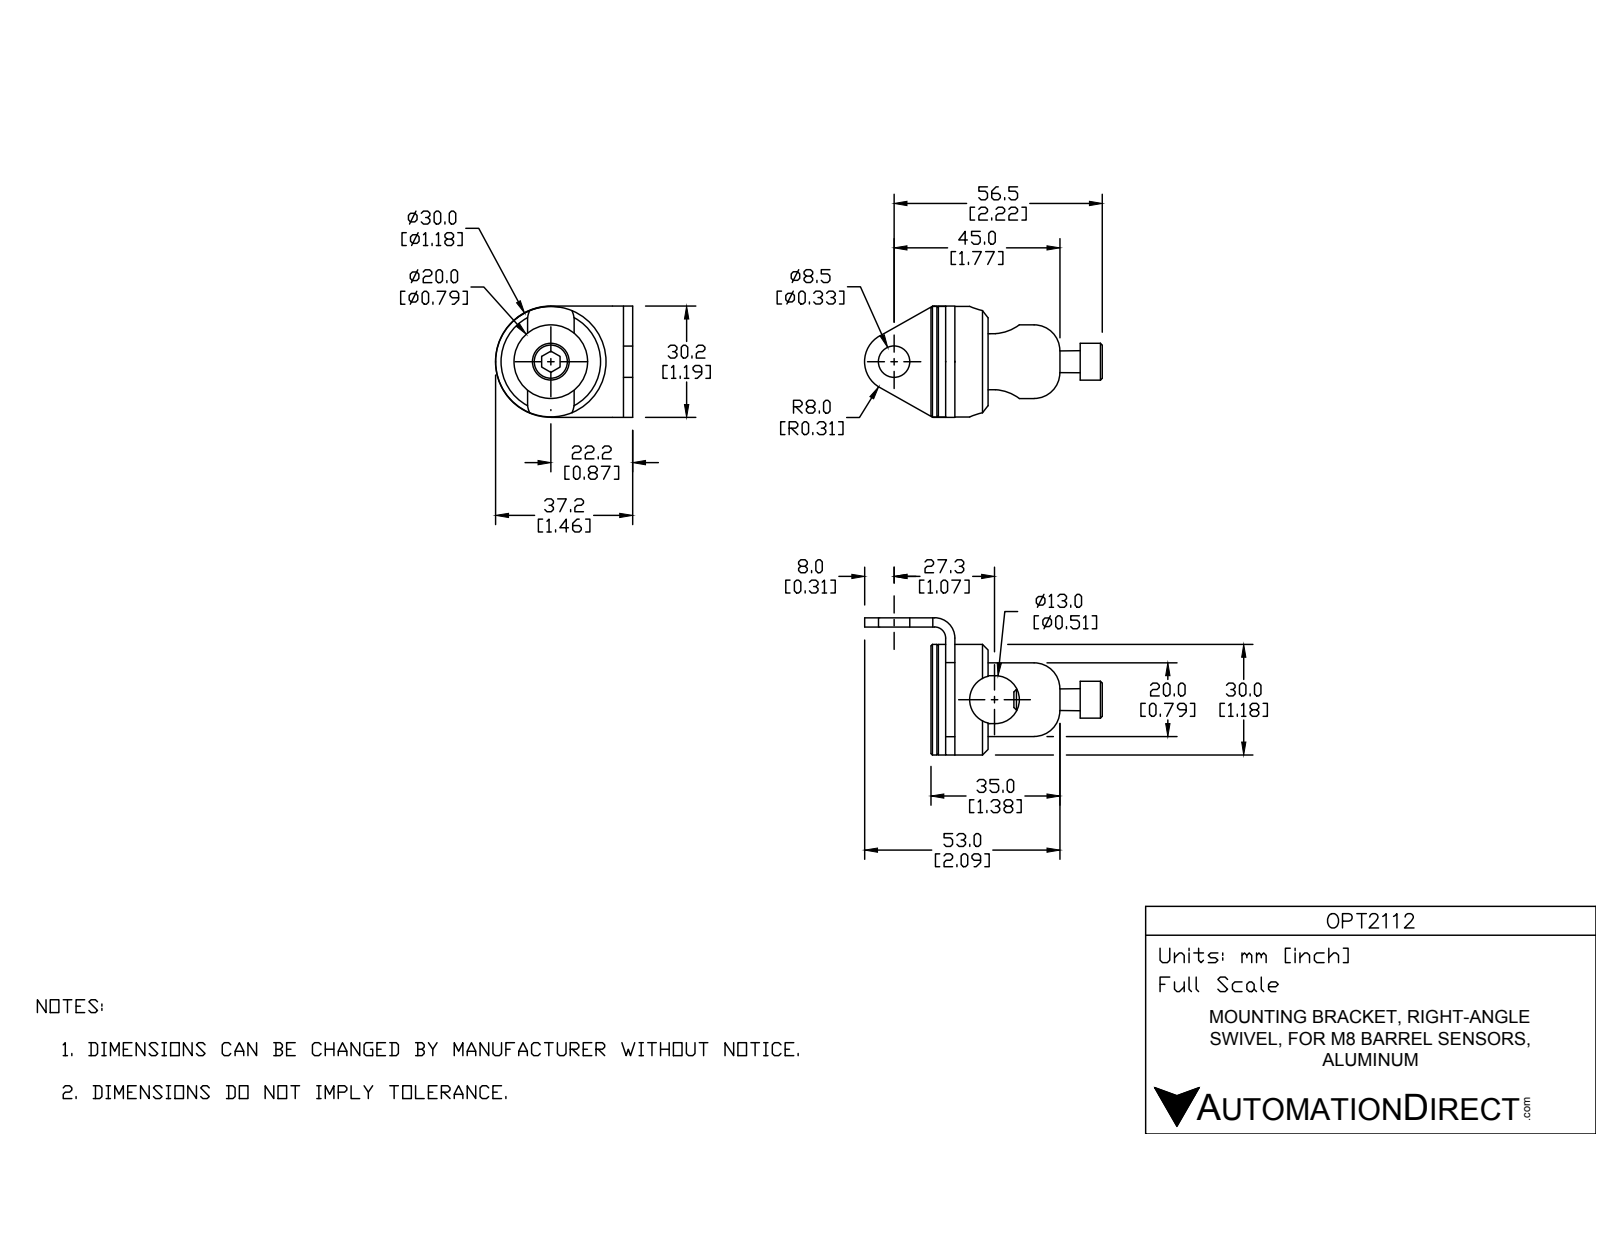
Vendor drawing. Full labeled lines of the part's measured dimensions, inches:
STEP written by: Unknown (CONFIG_CONTROL_DESIGN)
Units: inches
Bodies: 4 solids, 116 faces (58 planar, 40 cylindrical, 18 other)
Overall size (bounding box): 2.539 × 2.059 × 1.78
Volume: 1.864 in³ · Surface area: 26.46 in²
Round holes (diameter × count): ⌀0.335 ×2, ⌀0.791 ×2, ⌀0.787 ×1, ⌀0.827 ×1
Round bosses / shafts (diameter × count): ⌀1.181 ×1, ⌀0.394 ×1
Partial cylindrical surfaces — rounded edges, fillets, slot ends (radius × count): R0.591 ×4, R0.256 ×3, R0.118 ×2, R0.217 ×2, R0.315 ×2
Main face-to-face distances: 0.098, 0.157, 0.256, 0.059, 0.512, 0.354, 0.453, 0.61, 0.079, 0.02
Hole centre spacings: 1.057
